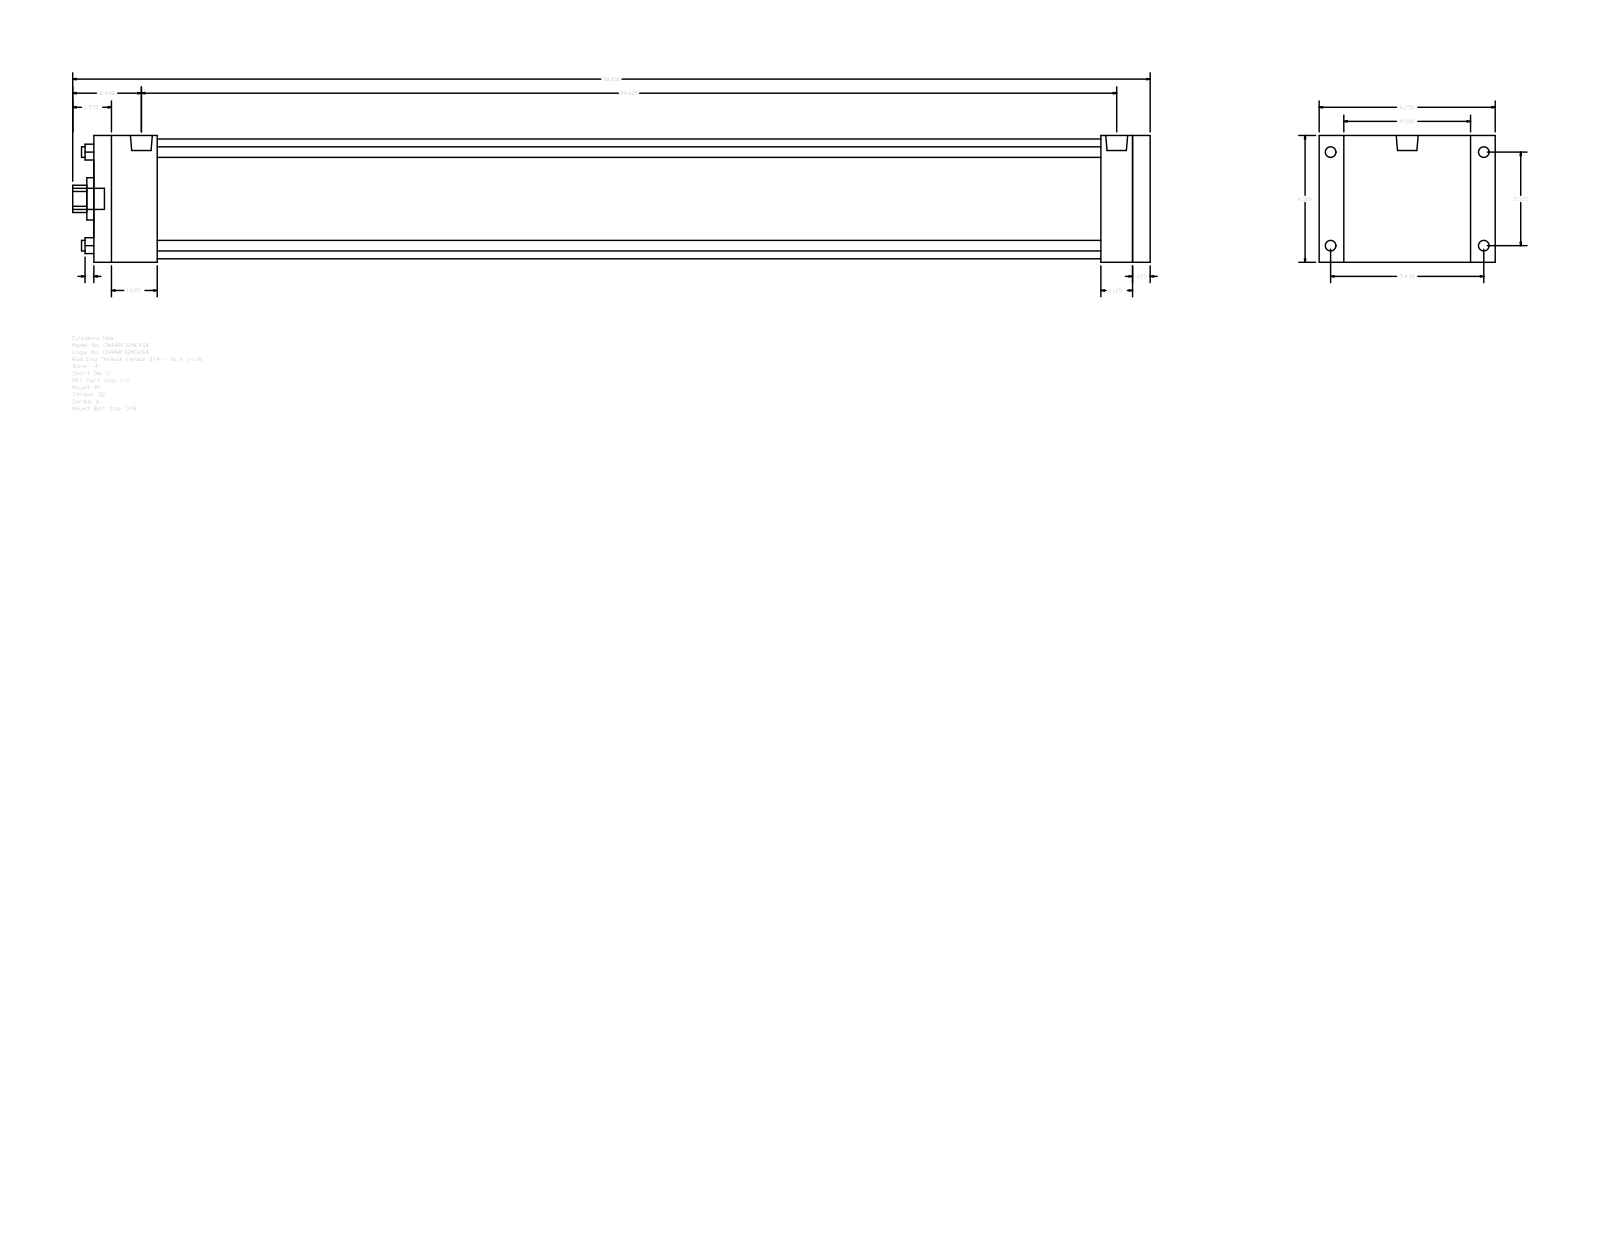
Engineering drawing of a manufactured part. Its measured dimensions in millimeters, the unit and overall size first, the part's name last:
Units: millimetres
Overall size (bounding box): 971.55 × 158.75 × 114.3
Round holes (diameter × count): ⌀9.53 ×4, ⌀25.4 ×1, ⌀38.1 ×1, ⌀107.95 ×1
Round bosses / shafts (diameter × count): ⌀9.53 ×4, ⌀8.73 ×4, ⌀19.77 ×2, ⌀19.05 ×1
Partial cylindrical surfaces — rounded edges, fillets, slot ends (radius × count): R12.29 ×1
Main face-to-face distances: 114.3, 952.5, 936.62, 15.88, 28.57, 22.23, 136.53, 908.05, 44.45, 57.15
Hole centre spacings: 59.62, 84.32, 119.25
Bodies: 0 solids, 92 faces (64 planar, 28 cylindrical, 0 other)
Part name (STEP PRODUCT): A_RF__0400_1
STEP written by: GSSL Pune (CONFIG_CONTROL_DESIGN)
